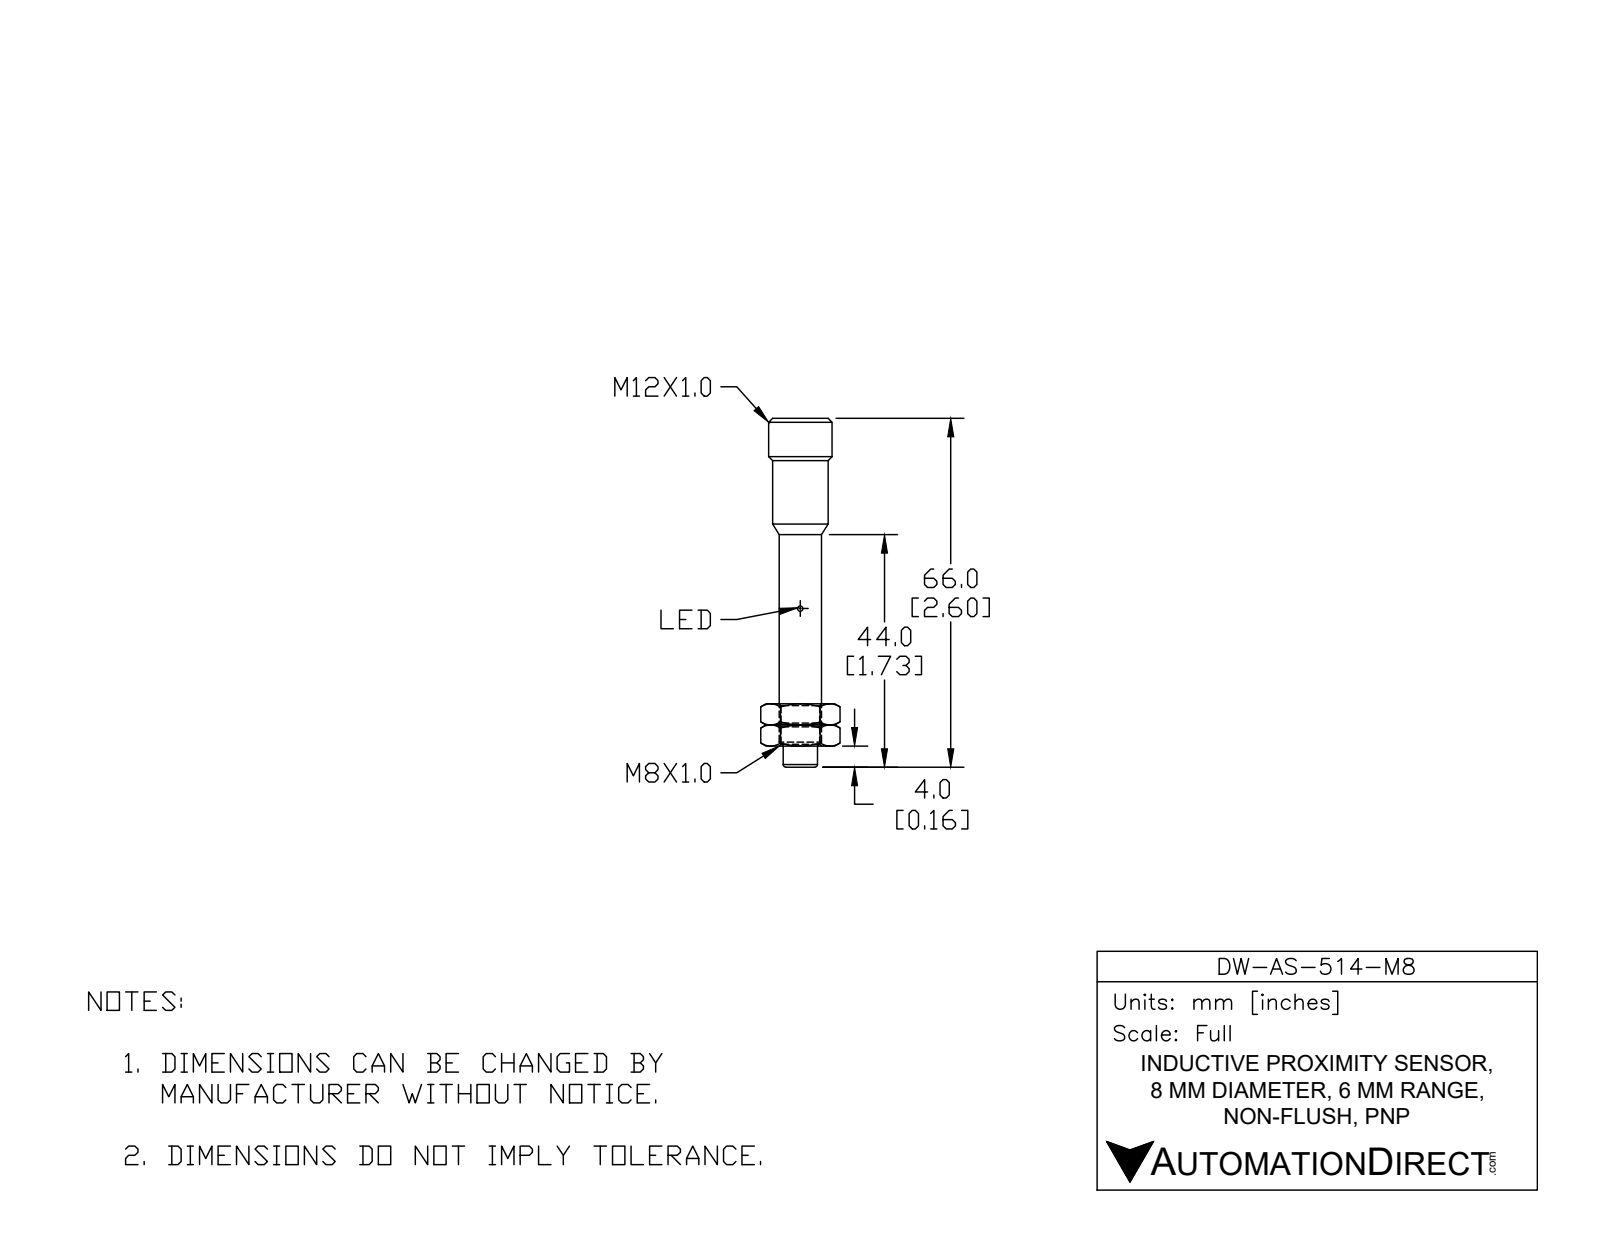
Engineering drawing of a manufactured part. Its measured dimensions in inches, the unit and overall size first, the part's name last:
Units: inches
Overall size (bounding box): 2.599 × 0.472 × 0.472
Round holes (diameter × count): ⌀0.12 ×2
Round bosses / shafts (diameter × count): ⌀0.039 ×4, ⌀0.472 ×1, ⌀0.415 ×1, ⌀0.335 ×1, ⌀0.315 ×1, ⌀0.272 ×1
Main face-to-face distances: 0.343, 2.256, 2.598, 1.811, 0.445, 0.787, 0.165, 1.646, 2.091, 2.433
Volume: 0.225 in³ · Surface area: 3.685 in²
Bodies: 1 solid, 35 faces (10 planar, 17 cylindrical, 8 other)
Part name (STEP PRODUCT): DW-AS-514-M8
STEP written by: SolidWorks 2017 (AUTOMOTIVE_DESIGN)
